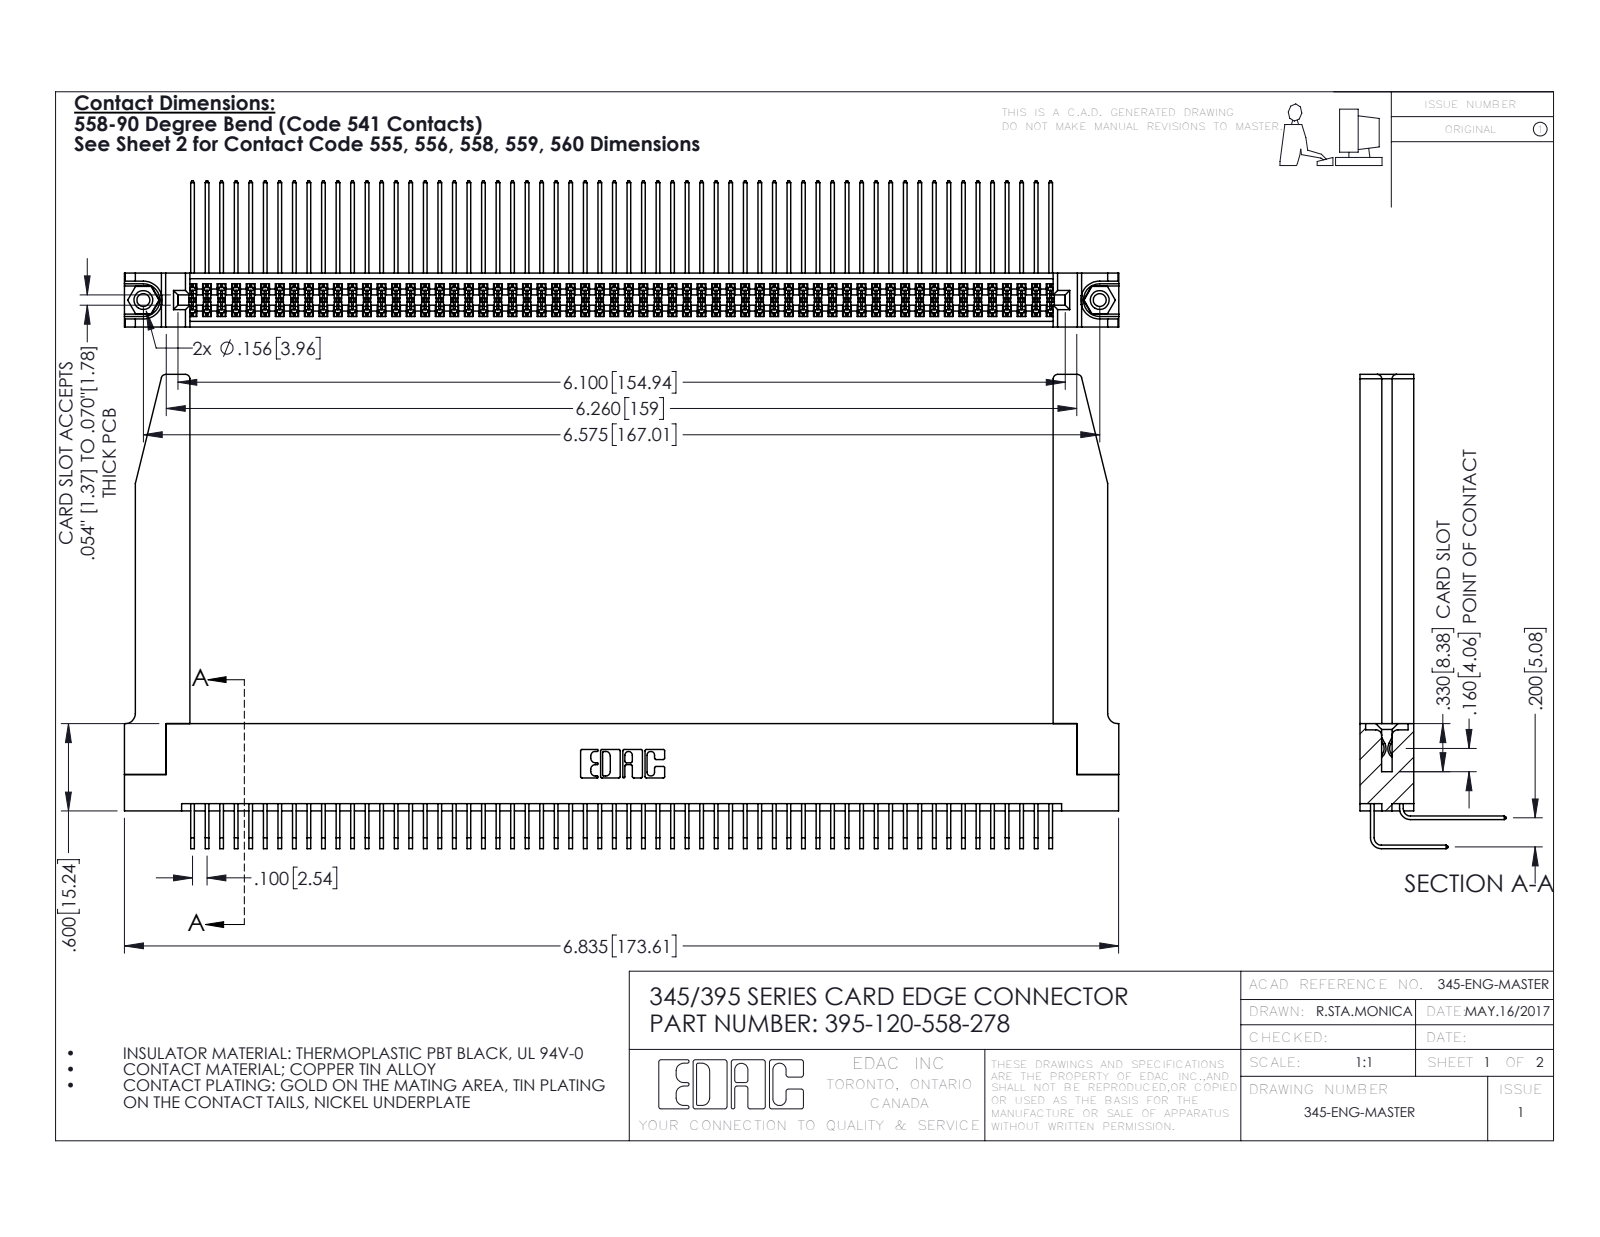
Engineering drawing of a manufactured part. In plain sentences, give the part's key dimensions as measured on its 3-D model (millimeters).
The part is named "345-250-001_345-250-001-102; 345 Part_Flush Mounting Lugs - 0.156 Dia-TH; 345-220-078_345-220-078; 395-120-558-278 (+2 more)". Its 3-D file was written by "SolidWorks 2016 (CONFIG_CONTROL_DESIGN)". It is 125 solids with 6600 faces: 4422 planar, 2126 cylindrical and 52 other. Overall it measures 173.6 by 82.8 by 25.5 millimeters. Its volume is 25 500 cubic millimeters and its surface area 36 650 square millimeters. Round holes: 2 of diameter 2.3, 2 of diameter 3.2, 2 of diameter 4, 1 of diameter 1.6. Round bosses or shafts: 2 of diameter 3.9. Partial cylindrical surfaces (rounded edges, fillets, slot ends): 181 of radius 0.2, 22 of radius 0.3, 8 of radius 0.8, 6 of radius 0.2, 6 of radius 0.8, 3 of radius 0.7, 2 of radius 0.4, 2 of radius 0.5. The main face-to-face distances are 1.8, 7.6, 9.4, 5.1, 2.5, 6.9, 0.6, 5.7, 0.6, 7.2. The hole center spacings are 6.9, 161, 167.
